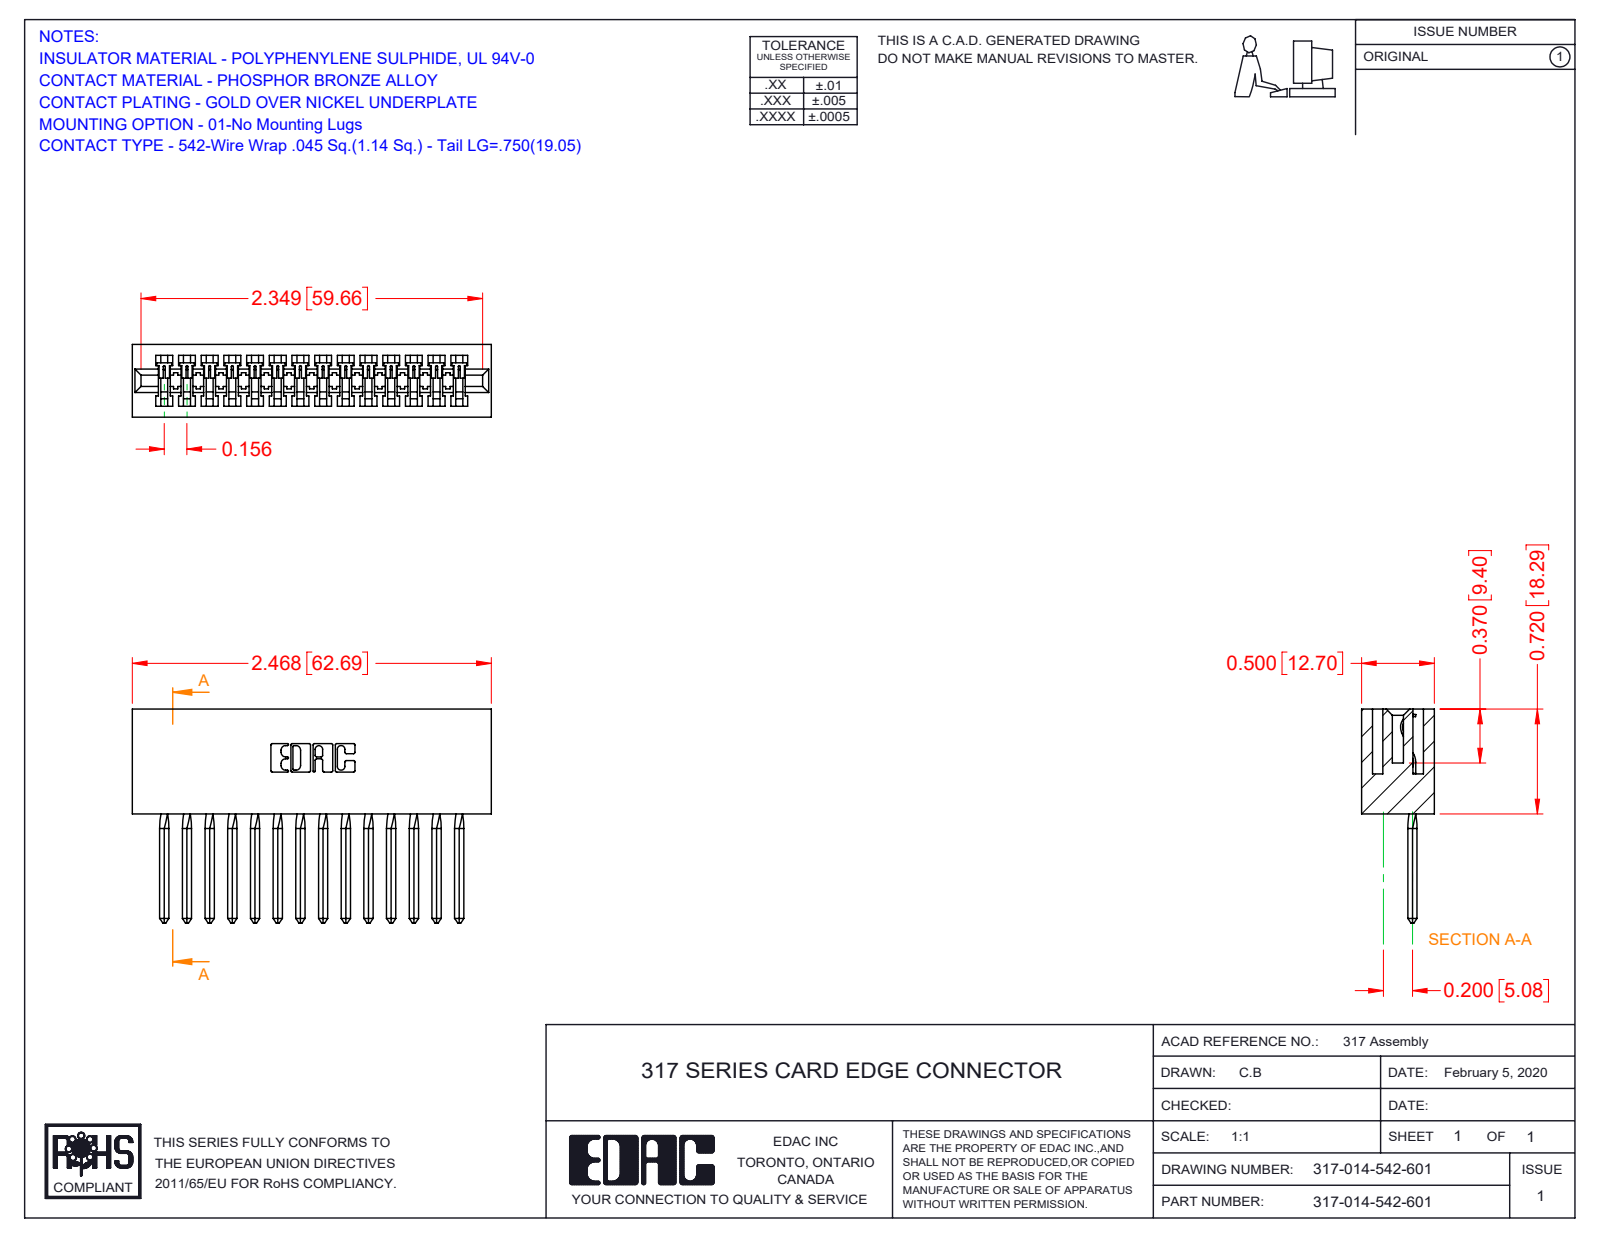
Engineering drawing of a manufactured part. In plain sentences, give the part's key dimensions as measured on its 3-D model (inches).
The part is named "317-014-542-601; 317 Part_Lugless; 317-290-003_542". Its 3-D file was written by "SolidWorks 2016 (CONFIG_CONTROL_DESIGN)". It is 15 solids with 1140 faces: 946 planar, 138 cylindrical and 56 other. Overall it measures 2.468 by 1.47 by 0.5 inches. Its volume is 0.642 cubic inches and its surface area 18.99 square inches. Partial cylindrical surfaces (rounded edges, fillets, slot ends): 28 of radius 0.006, 22 of radius 0.01, 6 of radius 0.007, 6 of radius 0.031, 3 of radius 0.026, 1 of radius 0.074, 1 of radius 0.089, 1 of radius 0.1. The main face-to-face distances are 0.5, 0.075, 0.425, 0.11, 0.35, 0.065, 0.156, 0.22, 0.136, 0.72.
